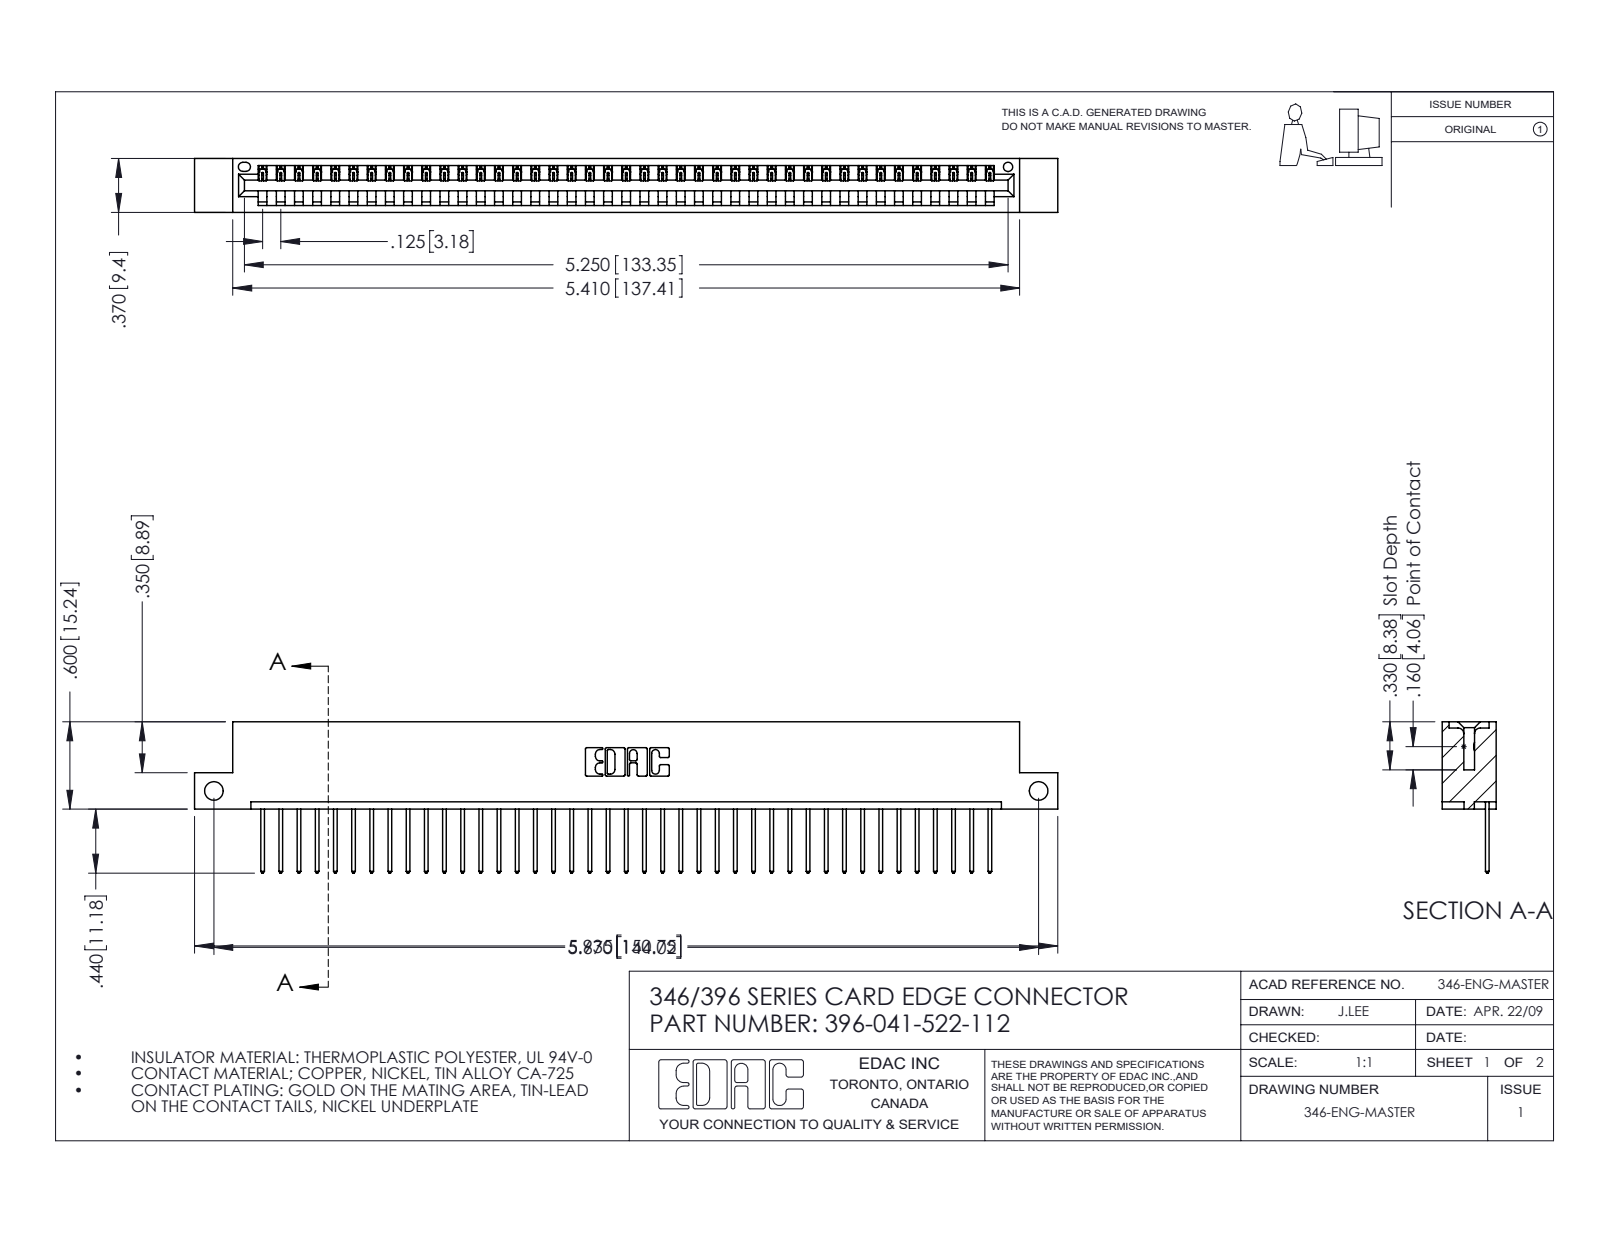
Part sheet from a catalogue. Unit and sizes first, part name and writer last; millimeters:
Units: millimetres
Overall size (bounding box): 150.7 × 26.4 × 9.4
Round holes (diameter × count): ⌀3.3 ×2, ⌀1.6 ×1
Partial cylindrical surfaces — rounded edges, fillets, slot ends (radius × count): R0.2 ×82, R0.3 ×82, R0.3 ×22, R0.2 ×6, R0.8 ×6, R0.7 ×3, R0.8 ×2, R1 ×2
Main face-to-face distances: 1.2, 8.2, 9.4, 6.4, 1.8, 7.6, 0.6, 3.8, 5.6, 2.5
Hole centre spacings: 144
Volume: 14 300 mm³ · Surface area: 17 920 mm²
Bodies: 42 solids, 2500 faces (1716 planar, 784 cylindrical, 0 other)
Part name (STEP PRODUCT): 346 Part_Flush Mounting Lugs - Side Mount; 345-292-001_345-293-122; 396-041-522-112
STEP written by: SolidWorks 2016 (CONFIG_CONTROL_DESIGN)
